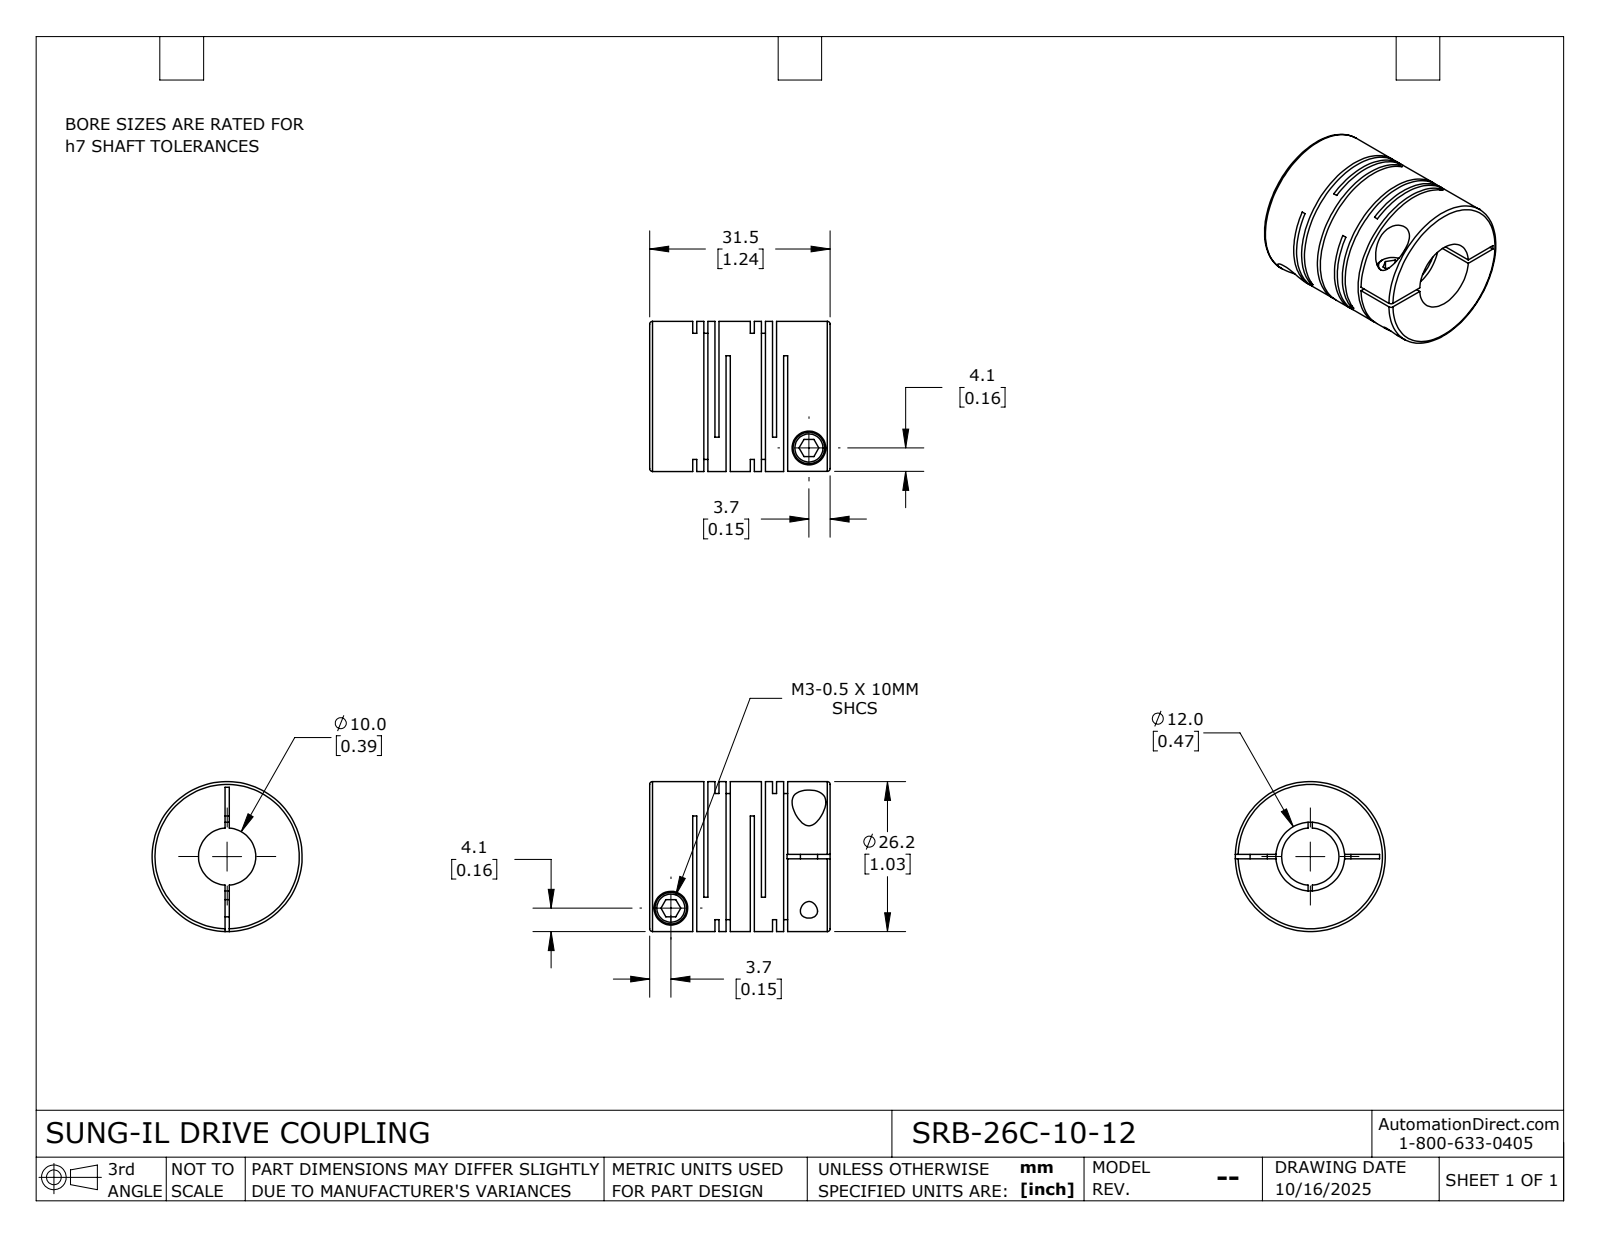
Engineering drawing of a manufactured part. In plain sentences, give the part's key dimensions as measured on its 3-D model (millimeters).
The part is named "SRB-26C-10-12". Its 3-D file was written by "SolidWorks 2024 (CONFIG_CONTROL_DESIGN)". It is 1 solid with 115 faces: 60 planar, 42 cylindrical and 13 other. Overall it measures 31.5 by 26.2 by 26.2 millimeters. Its volume is 11 320 cubic millimeters and its surface area 10 259 square millimeters. Round holes: 2 of diameter 3, 2 of diameter 5.9, 1 of diameter 10, 1 of diameter 12. Round bosses or shafts: 2 of diameter 5.5, 1 of diameter 26.2. The main face-to-face distances are 1.95, 10.05, 0.71, 3.9, 8.1, 12, 1.24, 2.66, 9.34, 13.95.
